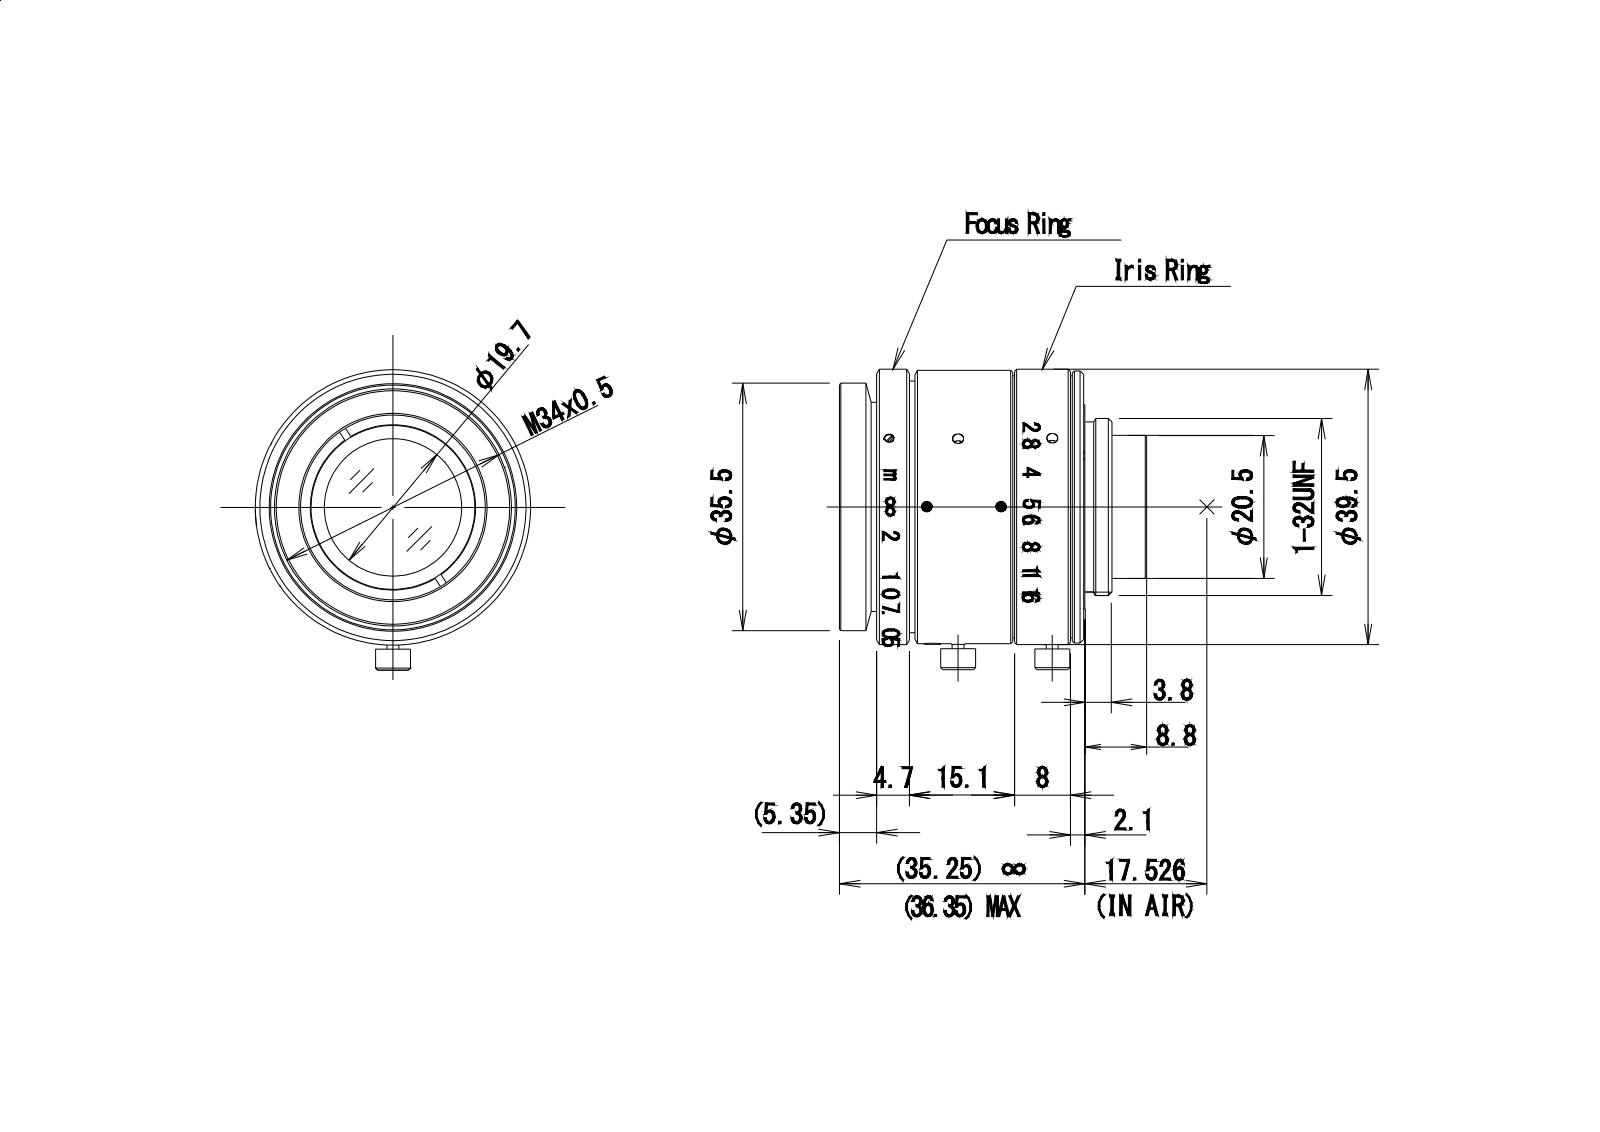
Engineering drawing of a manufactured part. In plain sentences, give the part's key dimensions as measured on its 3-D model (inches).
The part is named "Reference 3D-drawing of V1628-MPY2_16mm". Its 3-D file was written by "ST-DEVELOPER v16.7 (AUTOMOTIVE_DESIGN)". It is 1 solid with 276 faces: 164 planar, 68 cylindrical and 44 other. Overall it measures 1.778 by 1.697 by 1.556 inches. Its volume is 2.553 cubic inches and its surface area 14.48 square inches. Round holes: 5 of diameter 0.062, 3 of diameter 0.052, 3 of diameter 0.071, 3 of diameter 0.138, 1 of diameter 0.11, 1 of diameter 0.118, 1 of diameter 0.134, 1 of diameter 0.61, 1 of diameter 0.776, 1 of diameter 0.925, 1 of diameter 1.339. Round bosses or shafts: 6 of diameter 0.067, 4 of diameter 0.118, 2 of diameter 0.197, 2 of diameter 0.098, 1 of diameter 1.555, 1 of diameter 1.543, 1 of diameter 1.535, 1 of diameter 1.48. Partial cylindrical surfaces (rounded edges, fillets, slot ends): 1 of radius 0.026, 1 of radius 0.364, 1 of radius 0.522, 1 of radius 0.717. The main face-to-face distances are 1.169, 0.157, 1.326, 1.333, 1.175, 0.926, 0.342, 0.185, 0.984, 0.991. The hole center spacings are 0.642, 0.389, 0.532, 0.921, 1.111, 0.243, 1.112.
